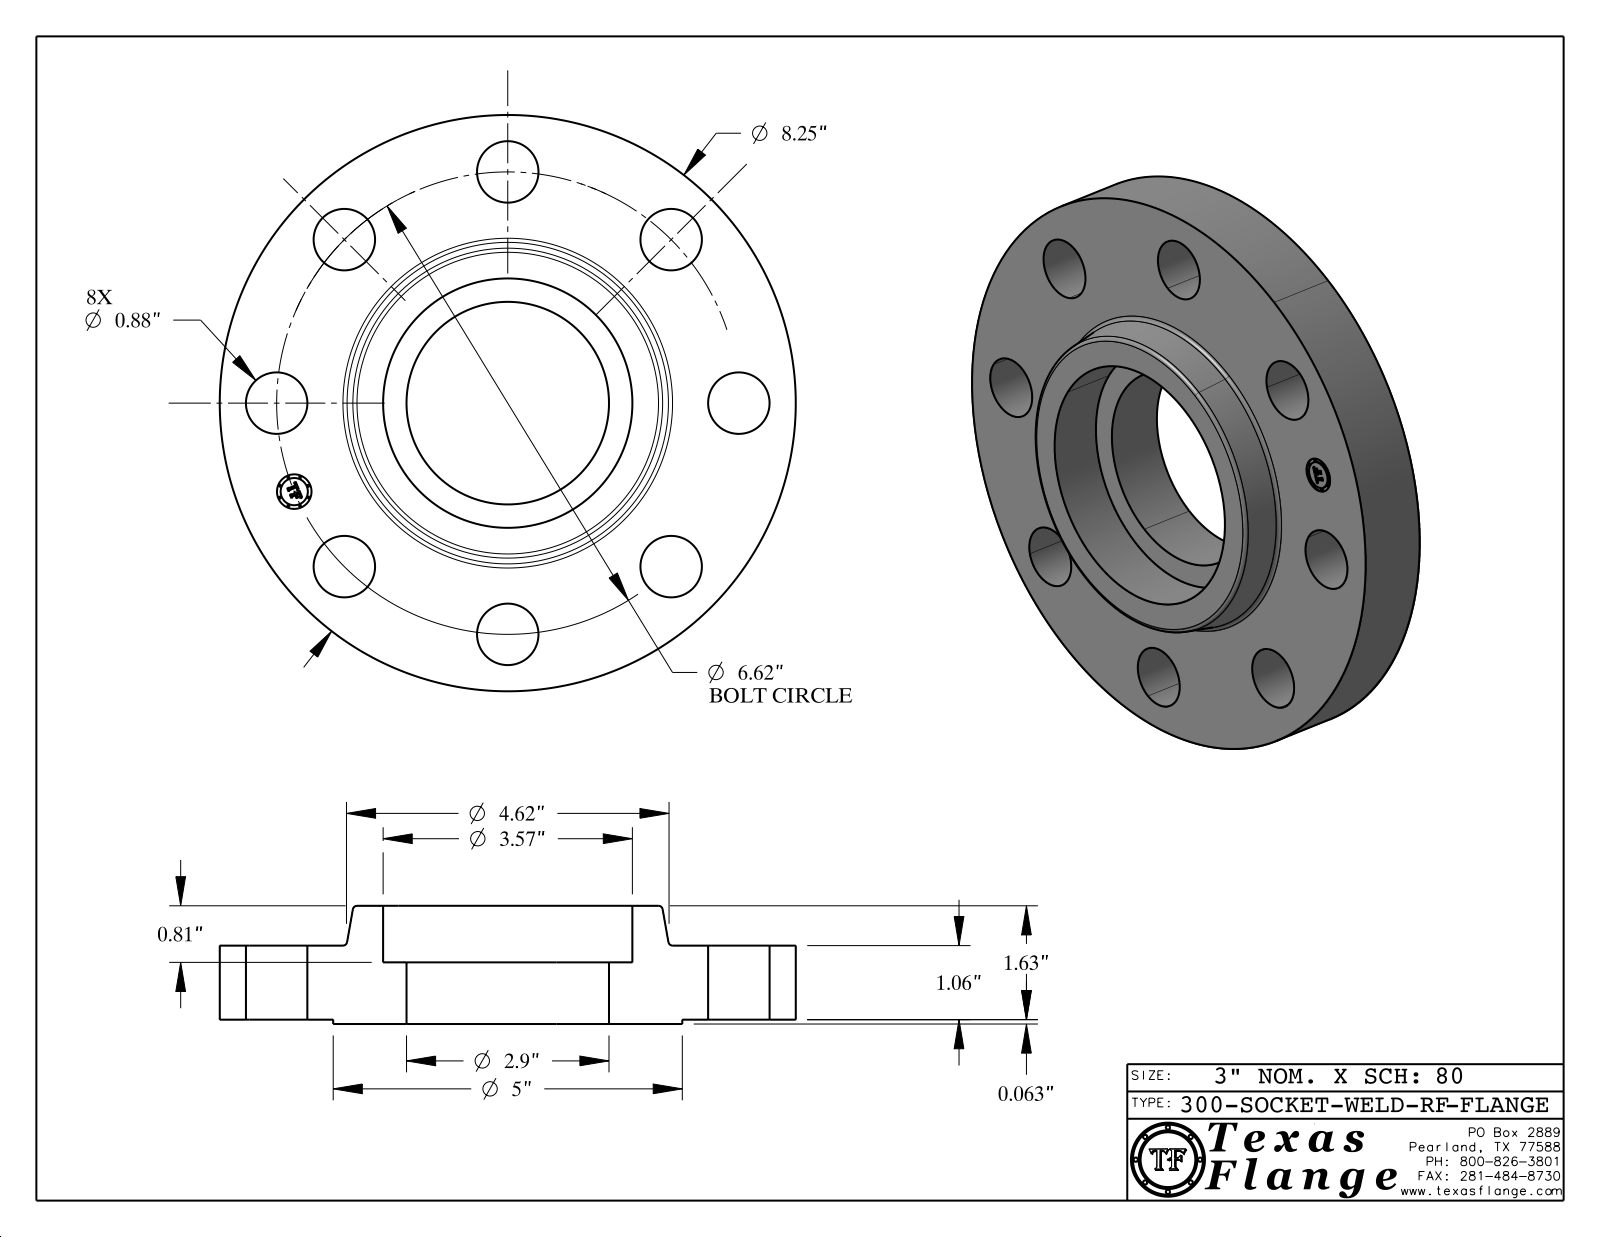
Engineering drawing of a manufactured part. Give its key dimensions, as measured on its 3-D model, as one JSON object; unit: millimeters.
{"part_name": "300-SOCKET-WELD-RF", "step_written_by": "CATIA V5 STEP AP214 (AUTOMOTIVE_DESIGN)", "units": "millimeters", "bodies": {"solids": 1, "faces": 420, "planar": 370, "cylindrical": 44, "other": 6}, "overall_size": [209.6, 209.6, 43], "volume_mm3": 785600, "surface_area_mm2": 102800, "round_holes": [[22.4, 8], [12.6, 1], [73.7, 1], [90.7, 1]], "round_bosses_or_shafts": [[0.8, 8], [209.6, 1], [127, 1], [9.9, 1]], "face_to_face_distances": [26.9, 1.6, 28.5, 43, 41.4, 14.5, 22.4, 20.8, 6.1, 20.6], "hole_center_spacings": [84.1, 64.3, 155.3, 118.9, 118.9, 32.8, 93.4, 164.9]}
